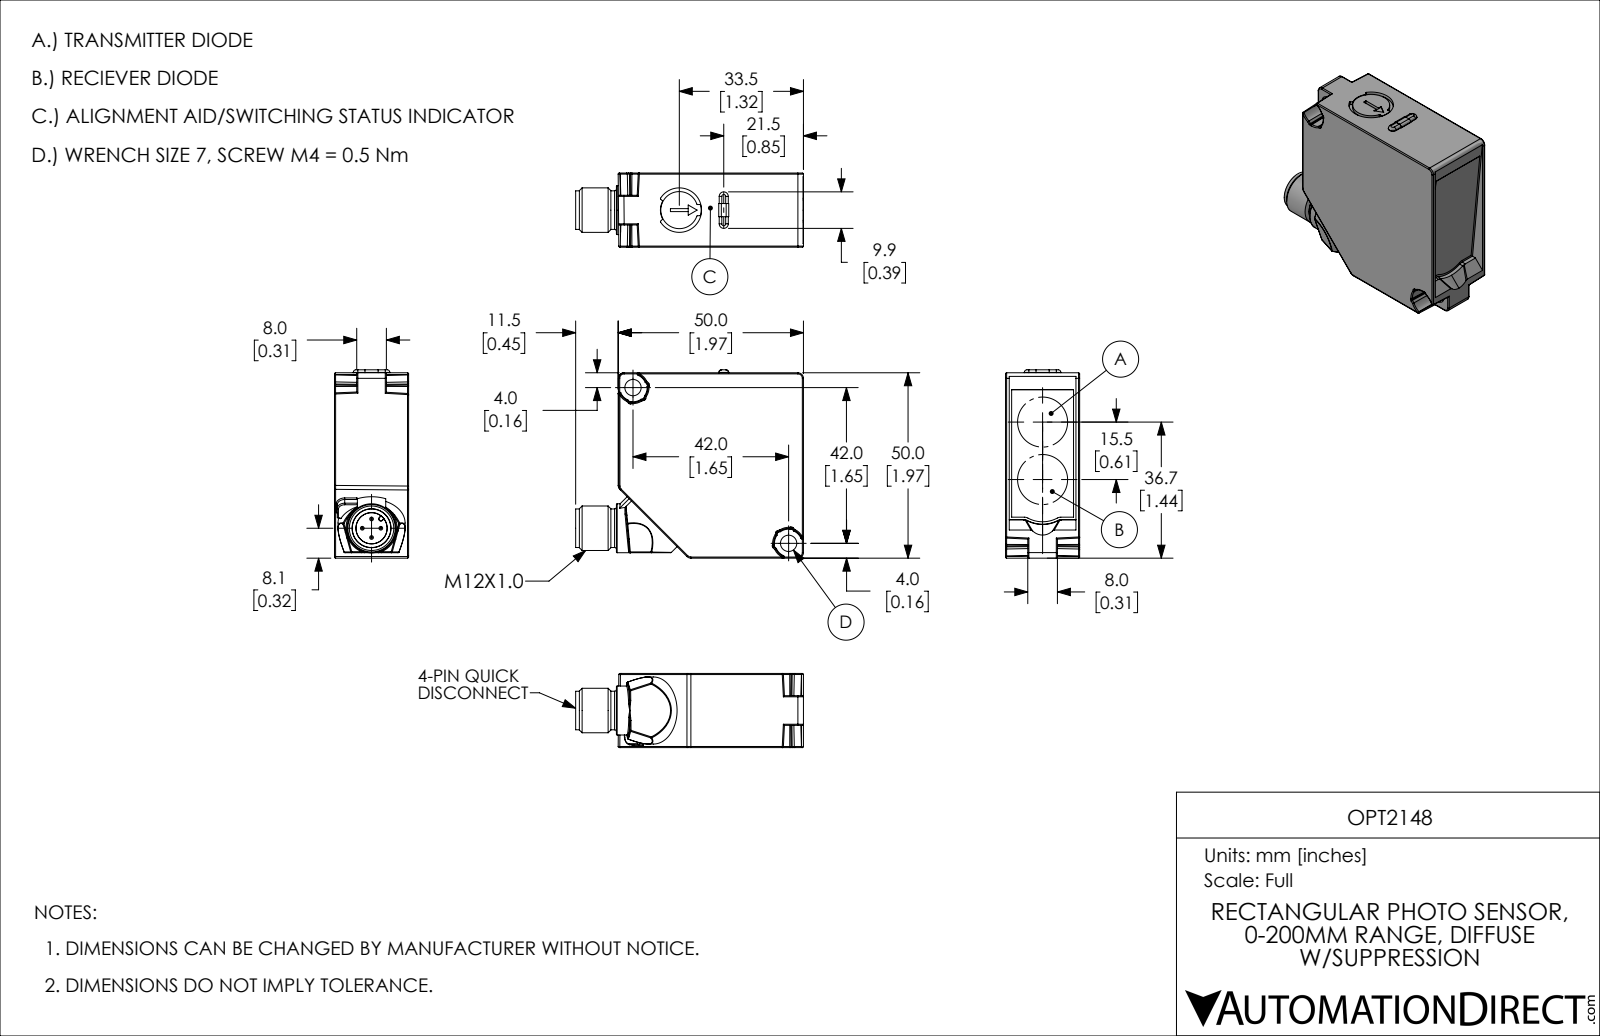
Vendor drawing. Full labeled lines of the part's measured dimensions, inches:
Part name (STEP PRODUCT): OPT2148
STEP written by: SolidWorks 2019 (AUTOMOTIVE_DESIGN)
Units: inches
Bodies: 1 solid, 342 faces (109 planar, 120 cylindrical, 113 other)
Overall size (bounding box): 2.42 × 2 × 0.787
Volume: 2.816 in³ · Surface area: 15.64 in²
Round holes (diameter × count): ⌀0.173 ×2, ⌀0.472 ×1, ⌀0.713 ×1
Round bosses / shafts (diameter × count): ⌀0.039 ×4, ⌀0.52 ×1, ⌀0.472 ×1, ⌀0.409 ×1, ⌀0.394 ×1
Partial cylindrical surfaces — rounded edges, fillets, slot ends (radius × count): R0.012 ×64, R0.008 ×8, R0.059 ×5, R0.079 ×5, R0.028 ×4, R0.048 ×2, R0.201 ×1, R0.232 ×1
Main face-to-face distances: 0.787, 1.969, 0.039, 0.748, 0.236, 0.551, 0.197, 0.512, 0.058, 1.911
Hole centre spacings: 2.339
